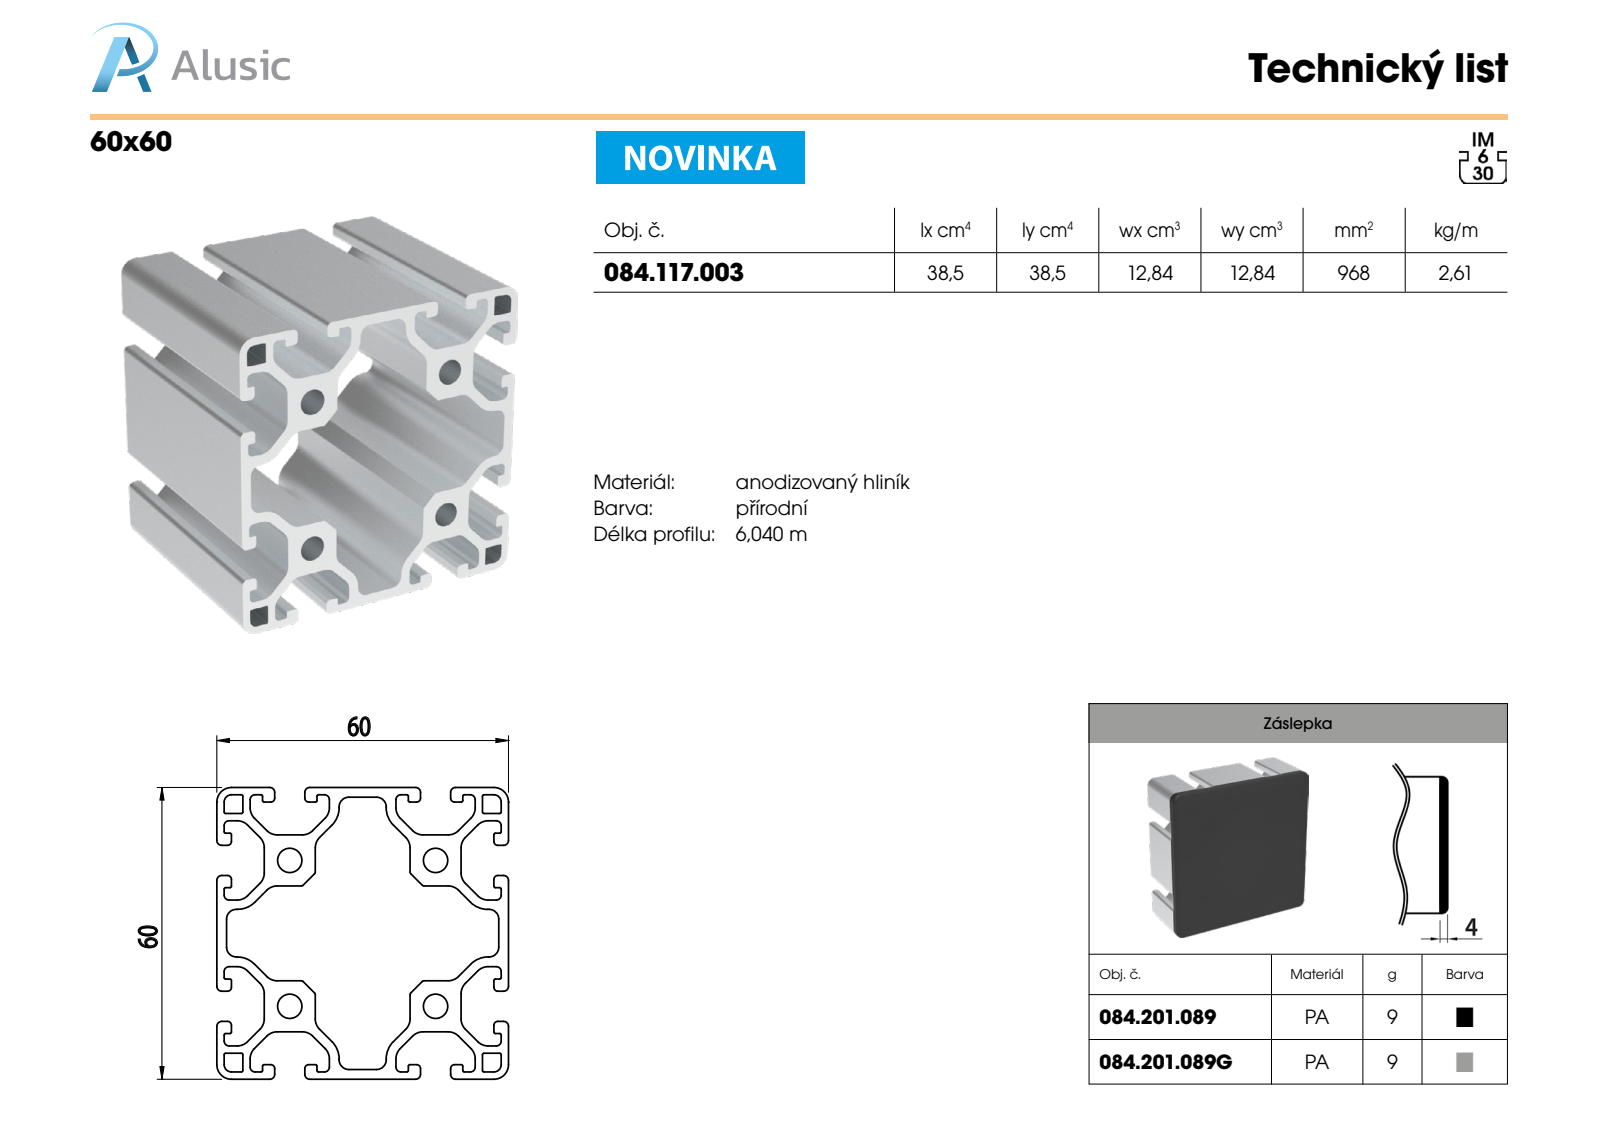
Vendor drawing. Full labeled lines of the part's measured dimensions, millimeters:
Part name (STEP PRODUCT): 084.117.003
STEP written by: SolidWorks 2018 (AUTOMOTIVE_DESIGN)
Units: millimetres
Bodies: 1 solid, 338 faces (166 planar, 172 cylindrical, 0 other)
Overall size (bounding box): 100 × 60 × 60
Volume: 96 795 mm³ · Surface area: 85 733 mm²
Round holes (diameter × count): ⌀5 ×4
Partial cylindrical surfaces — rounded edges, fillets, slot ends (radius × count): R0.3 ×44, R3 ×44, R1 ×32, R0.8 ×16, R0.5 ×8, R2 ×8, R5 ×8, R1.5 ×4
Main face-to-face distances: 60, 1.5, 2, 21.21, 30, 50.25, 9.75, 57, 20.25, 39.75
Hole centre spacings: 30, 42.43
